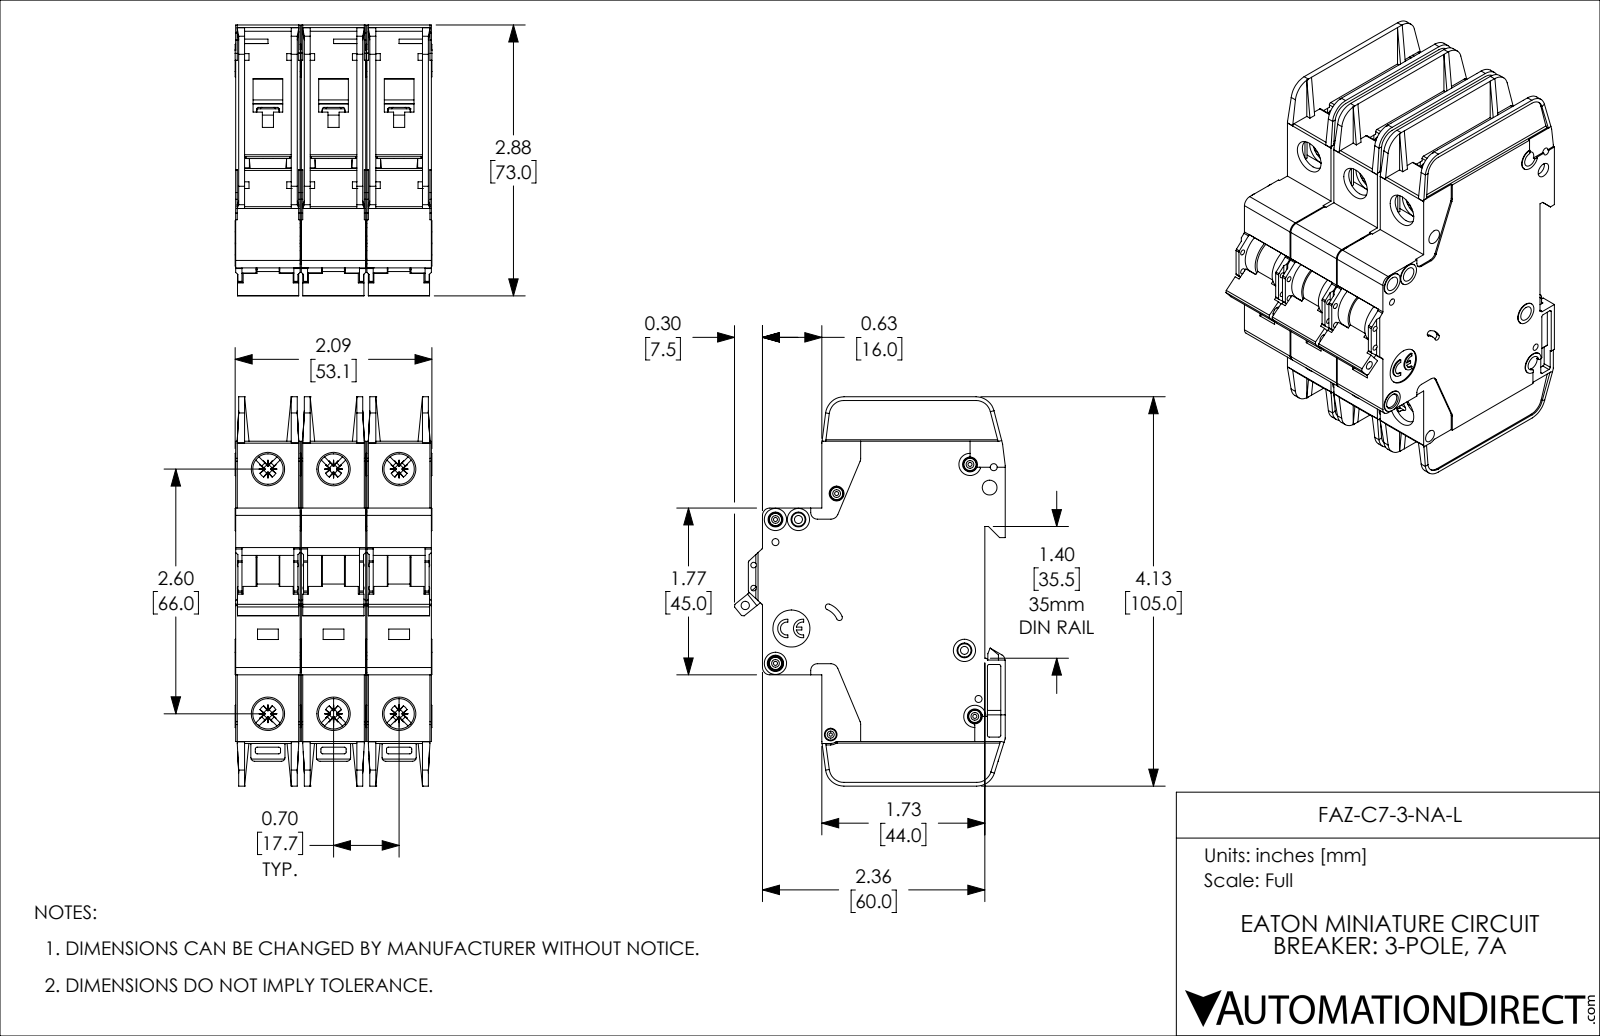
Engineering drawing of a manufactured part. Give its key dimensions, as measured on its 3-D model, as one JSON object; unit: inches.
{"part_name": "FAZ-C7-3-NA-L", "step_written_by": "SolidWorks 2019 (AUTOMOTIVE_DESIGN)", "units": "inches", "bodies": {"solids": 3, "faces": 3381, "planar": 2013, "cylindrical": 1071, "other": 297}, "overall_size": [4.134, 2.876, 2.091], "volume_in3": 14.05, "surface_area_in2": 123, "round_holes": [[0.157, 8], [0.323, 6], [0.043, 5], [0.075, 4], [0.059, 2], [0.085, 2], [0.035, 1], [0.089, 1], [0.098, 1], [0.134, 1], [0.394, 1]], "round_bosses_or_shafts": [[0.13, 5], [0.236, 4], [0.118, 4], [0.098, 3]], "partial_cylinders_radius": [[0.02, 72], [0.016, 30], [0.039, 18], [0.043, 12], [0.079, 12], [0.008, 6], [0.01, 6], [0.028, 6]], "face_to_face_distances": [0.697, 0.047, 1.394, 0.685, 0.591, 1.382, 0.744, 0.65, 0.106, 0.094], "hole_center_spacings": [0.697, 2.69, 2.598, 0.244, 0.537, 0.87, 1.394, 2.948]}
